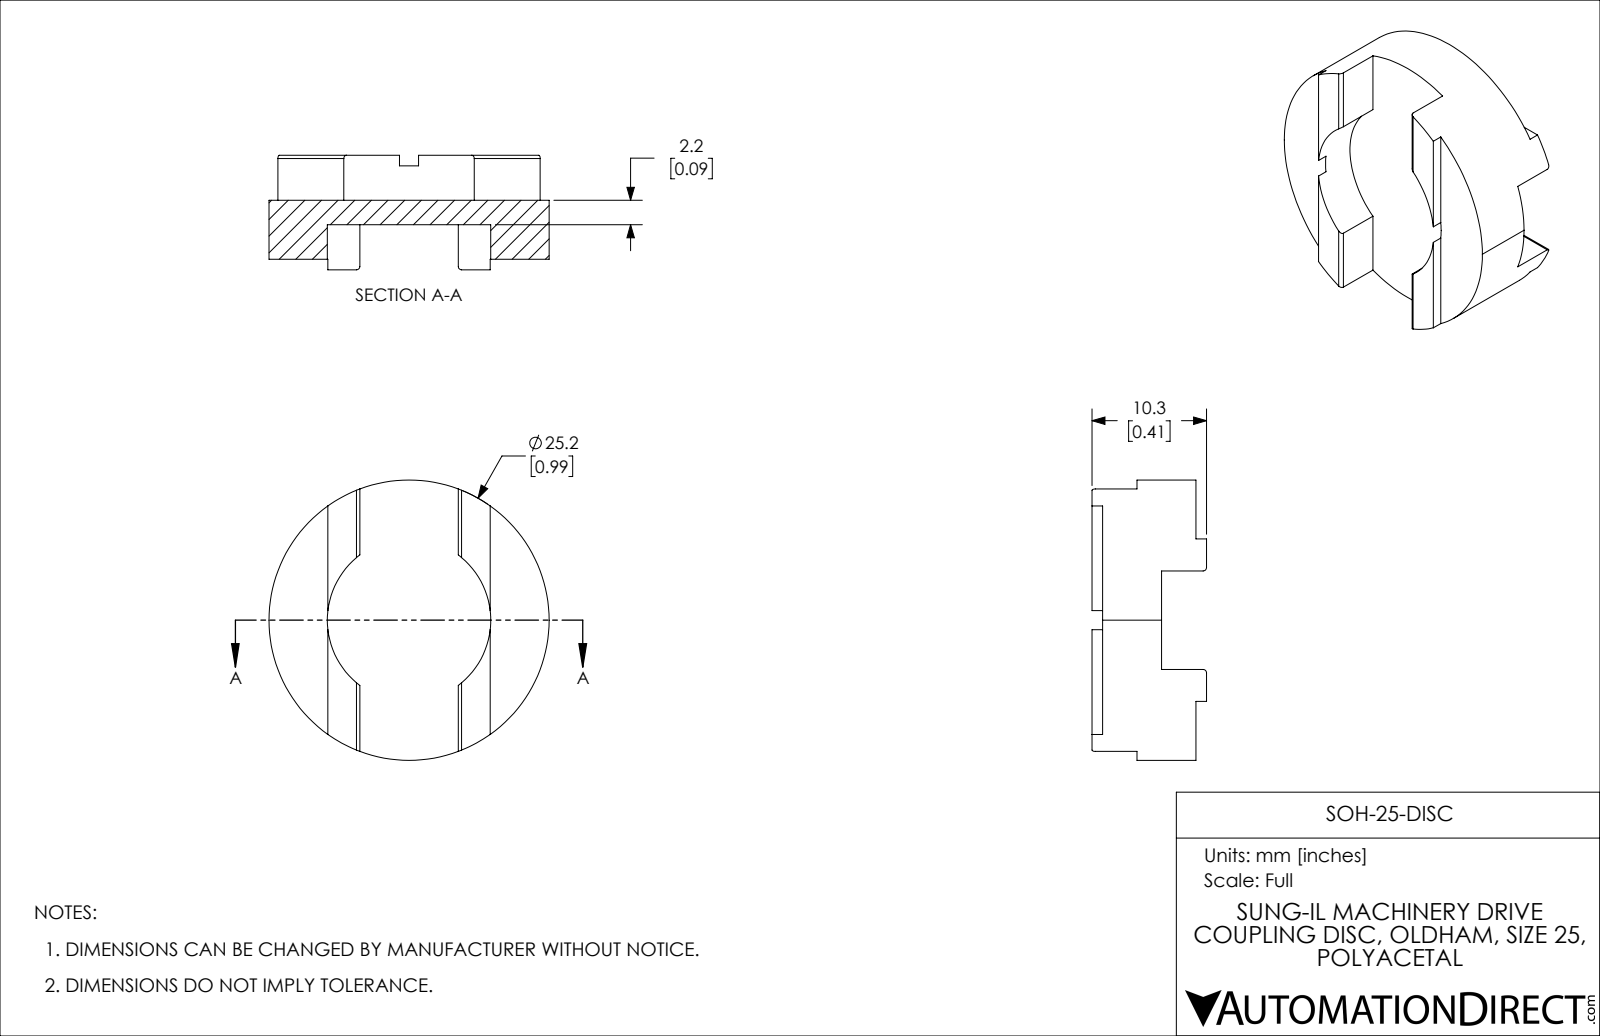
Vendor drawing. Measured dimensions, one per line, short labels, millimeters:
name: SOH-25-DISC
written by: SolidWorks 2021 (CONFIG_CONTROL_DESIGN)
unit: mm
bodies: 1 solid, 45 faces (30 planar, 15 cylindrical, 0 other)
size: 25.2 × 25.2 × 10.3
volume: 2 688 mm³; area: 2 046 mm²
holes: 1× ⌀14.7
bosses: 1× ⌀25.2
rounds: 4× R0.3
face distances: 3.1, 5.3, 2.2, 8.4, 0.95, 4.05, 6.25, 9.35, 8.86, 10.3
